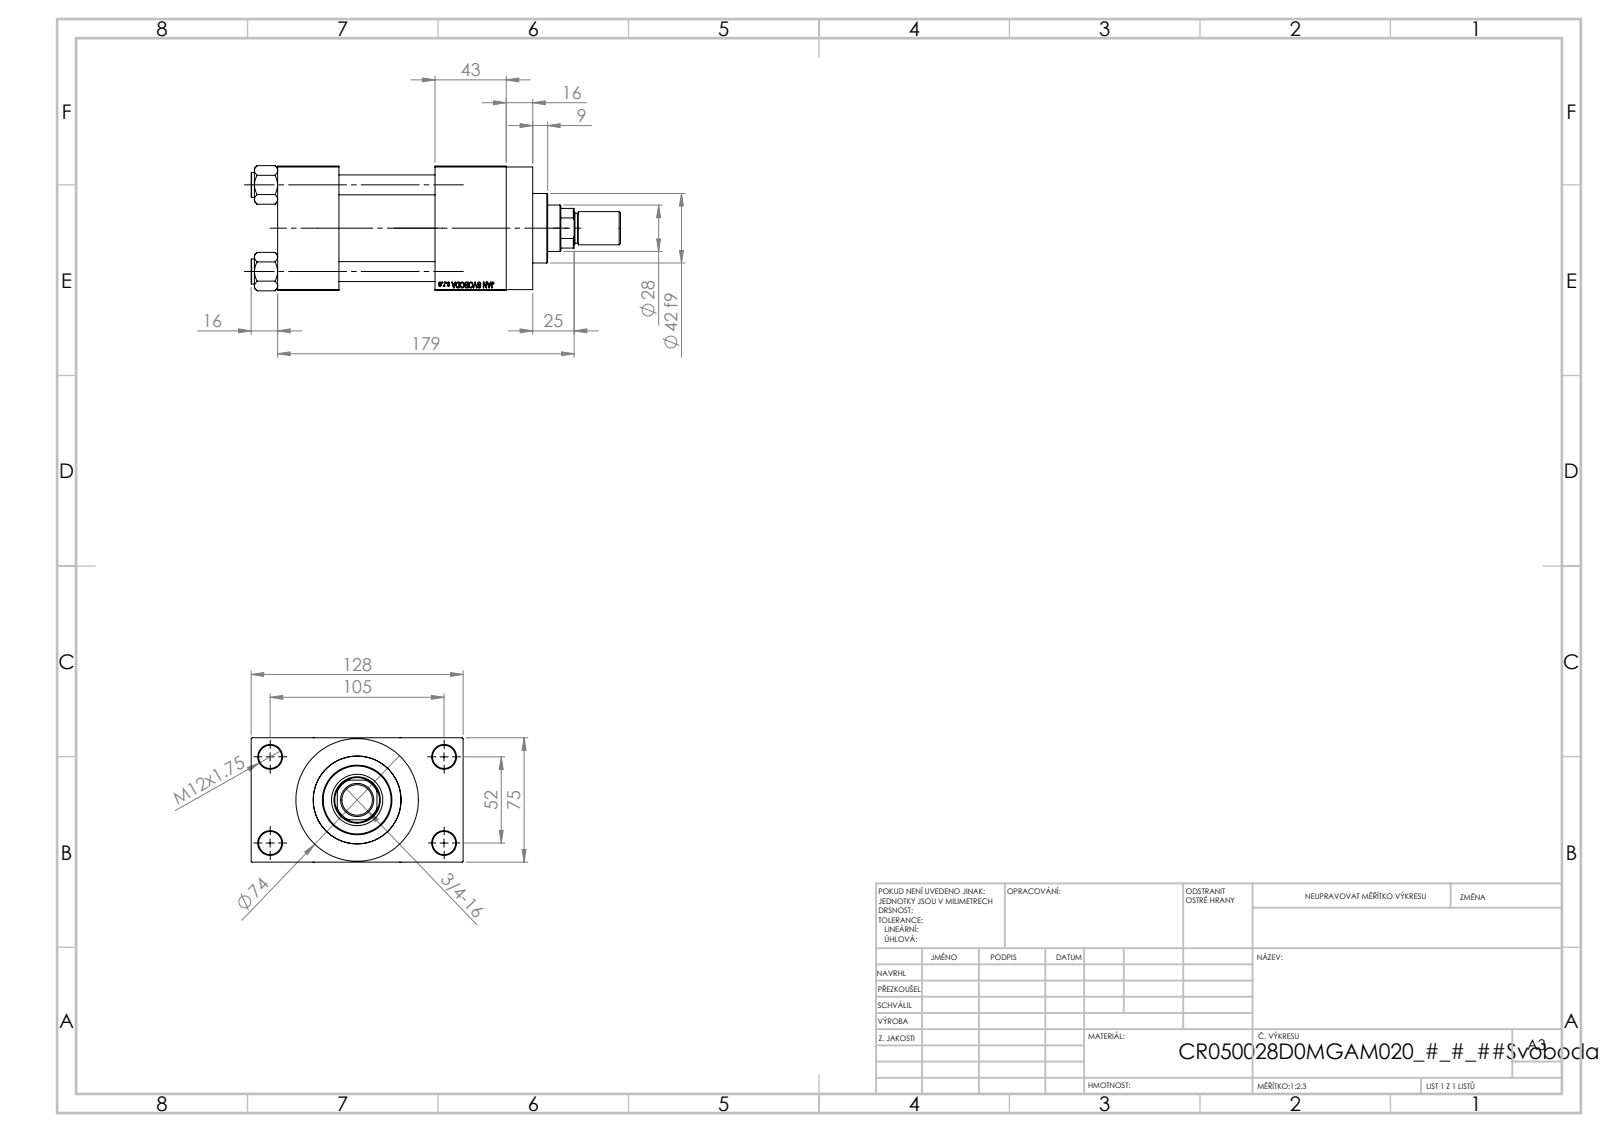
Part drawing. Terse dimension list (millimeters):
name: V215CR_D_Body; NUT_M5_D; V215CR_D_TYCINKA; ROD_END_AH (+2 more)
written by: SolidWorks 2019 (CONFIG_CONTROL_DESIGN)
unit: mm
bodies: 12 solids, 1118 faces (501 planar, 93 cylindrical, 524 other)
size: 223 × 128 × 75.54
volume: 823 884 mm³; area: 171 302 mm²
holes: 4× ⌀12, 4× ⌀14, 2× ⌀7, 2× ⌀20.96, 2× ⌀30, 1× ⌀18.5, 1× ⌀28, 1× ⌀31, 1× ⌀41, 1× ⌀50, 1× ⌀53
bosses: 4× ⌀15, 1× ⌀74, 1× ⌀56, 1× ⌀42, 1× ⌀20, 1× ⌀18
rounds: 1× R13.5
face distances: 75, 58, 37, 95, 26.5, 101.5, 138, 101, 43, 16
hole spacings: 26.35, 36.98, 52.3, 58.43, 58.59, 78.65, 94.37, 52
